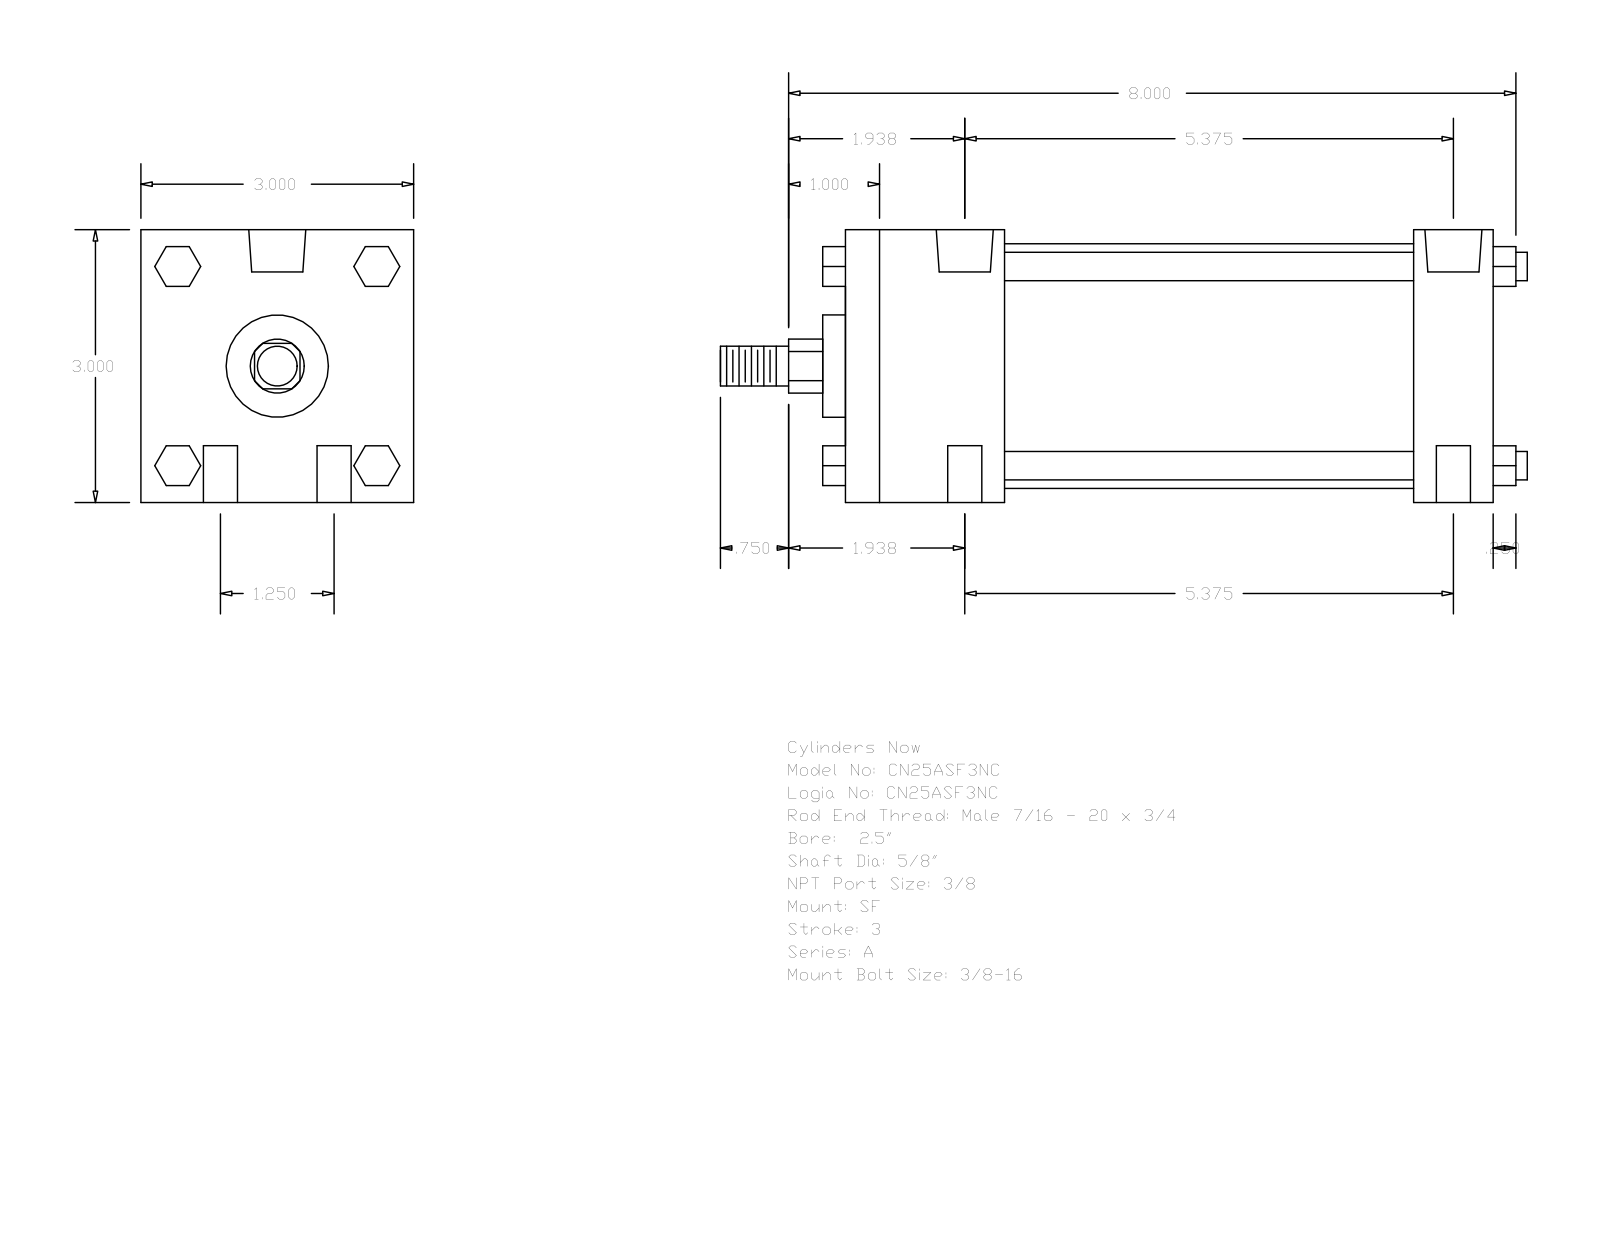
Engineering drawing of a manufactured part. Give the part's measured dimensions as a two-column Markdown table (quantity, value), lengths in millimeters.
| quantity | value |
| --- | --- |
| part name | A_SF__0250_0.625 |
| STEP written by | GSSL Pune (CONFIG_CONTROL_DESIGN) |
| units | millimeters |
| bodies | 0 solids, 124 faces (94 planar, 30 cylindrical, 0 other) |
| overall size | 225.43 × 76.2 × 76.2 |
| round holes (diameter × count) | 9.53 × 4, 5.56 × 2, 15.93 × 2 |
| round bosses / shafts (diameter × count) | 7.94 × 4, 68.33 × 1, 28.57 × 1, 15.88 × 1, 11.11 × 1 |
| partial cylindrical surfaces (radius × count) | 7.54 × 1 |
| main face-to-face distances | 76.2, 180.97, 44.45, 158.74, 22.23, 114.29, 136.52, 6.35, 187.32, 50.8 |
| hole center spacings | 15.88, 137.45, 136.53, 31.76, 140.18, 141.29 |
